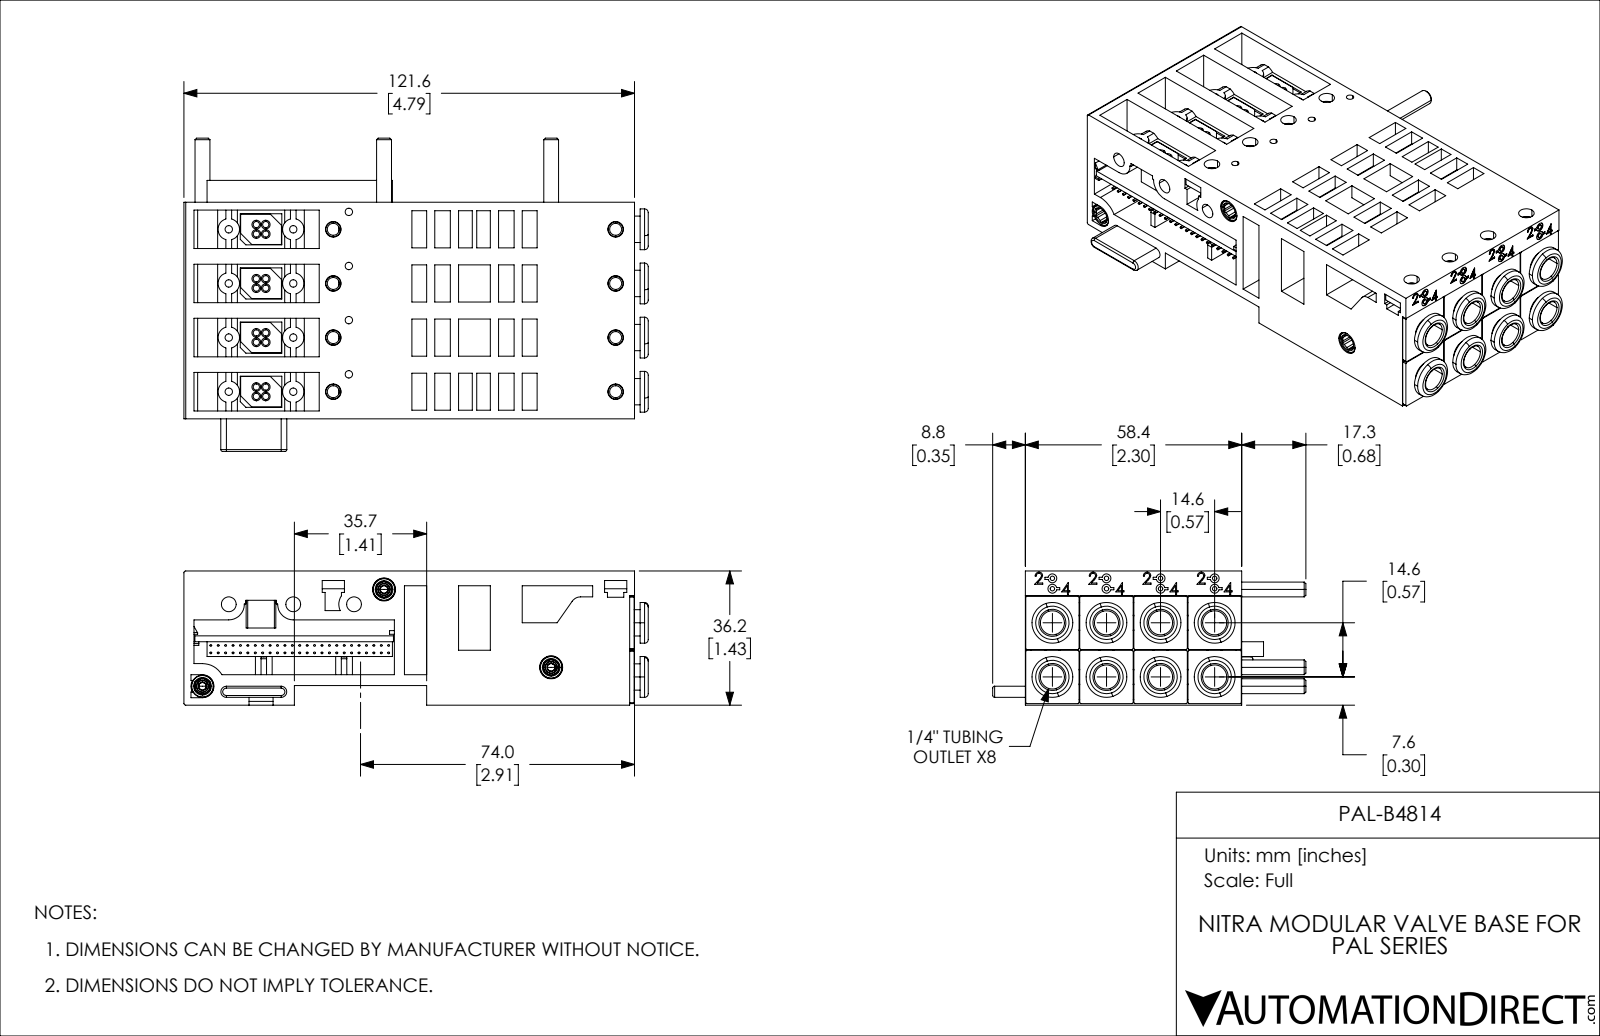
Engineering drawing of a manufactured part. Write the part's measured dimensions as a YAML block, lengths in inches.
part_name: "PAL-B4814"
step_written_by: "SolidWorks 2019 (CONFIG_CONTROL_DESIGN)"
units: inches
bodies: {solids: 7, faces: 1710, planar: 930, cylindrical: 586, other: 194}
overall_size: [4.933, 3.327, 1.425]
volume: 9.472
surface_area: 128.5
round_holes:
  - {diameter: 0.02, count: 50}
  - {diameter: 0.079, count: 12}
  - {diameter: 0.128, count: 11}
  - {diameter: 0.094, count: 8}
  - {diameter: 0.165, count: 8}
  - {diameter: 0.256, count: 8}
  - {diameter: 0.157, count: 3}
  - {diameter: 0.244, count: 2}
  - {diameter: 0.189, count: 1}
round_bosses_or_shafts:
  - {diameter: 0.433, count: 8}
  - {diameter: 0.28, count: 8}
  - {diameter: 0.228, count: 8}
  - {diameter: 0.047, count: 8}
  - {diameter: 0.236, count: 3}
  - {diameter: 0.157, count: 3}
  - {diameter: 0.177, count: 2}
partial_cylinders:
  - {radius: 0.02, count: 11}
  - {radius: 0.098, count: 8}
  - {radius: 0.295, count: 8}
  - {radius: 0.394, count: 8}
  - {radius: 0.157, count: 6}
  - {radius: 0.037, count: 5}
  - {radius: 0.039, count: 5}
  - {radius: 0.026, count: 4}
face_to_face_distances: [1.425, 0.063, 0.323, 0.752, 0.673, 0.736, 0.575, 0.413, 0.339, 0.689]
hole_center_spacings: [0.575, 0.079, 0.157, 0.236, 0.315, 0.472, 1.15, 0.394]
